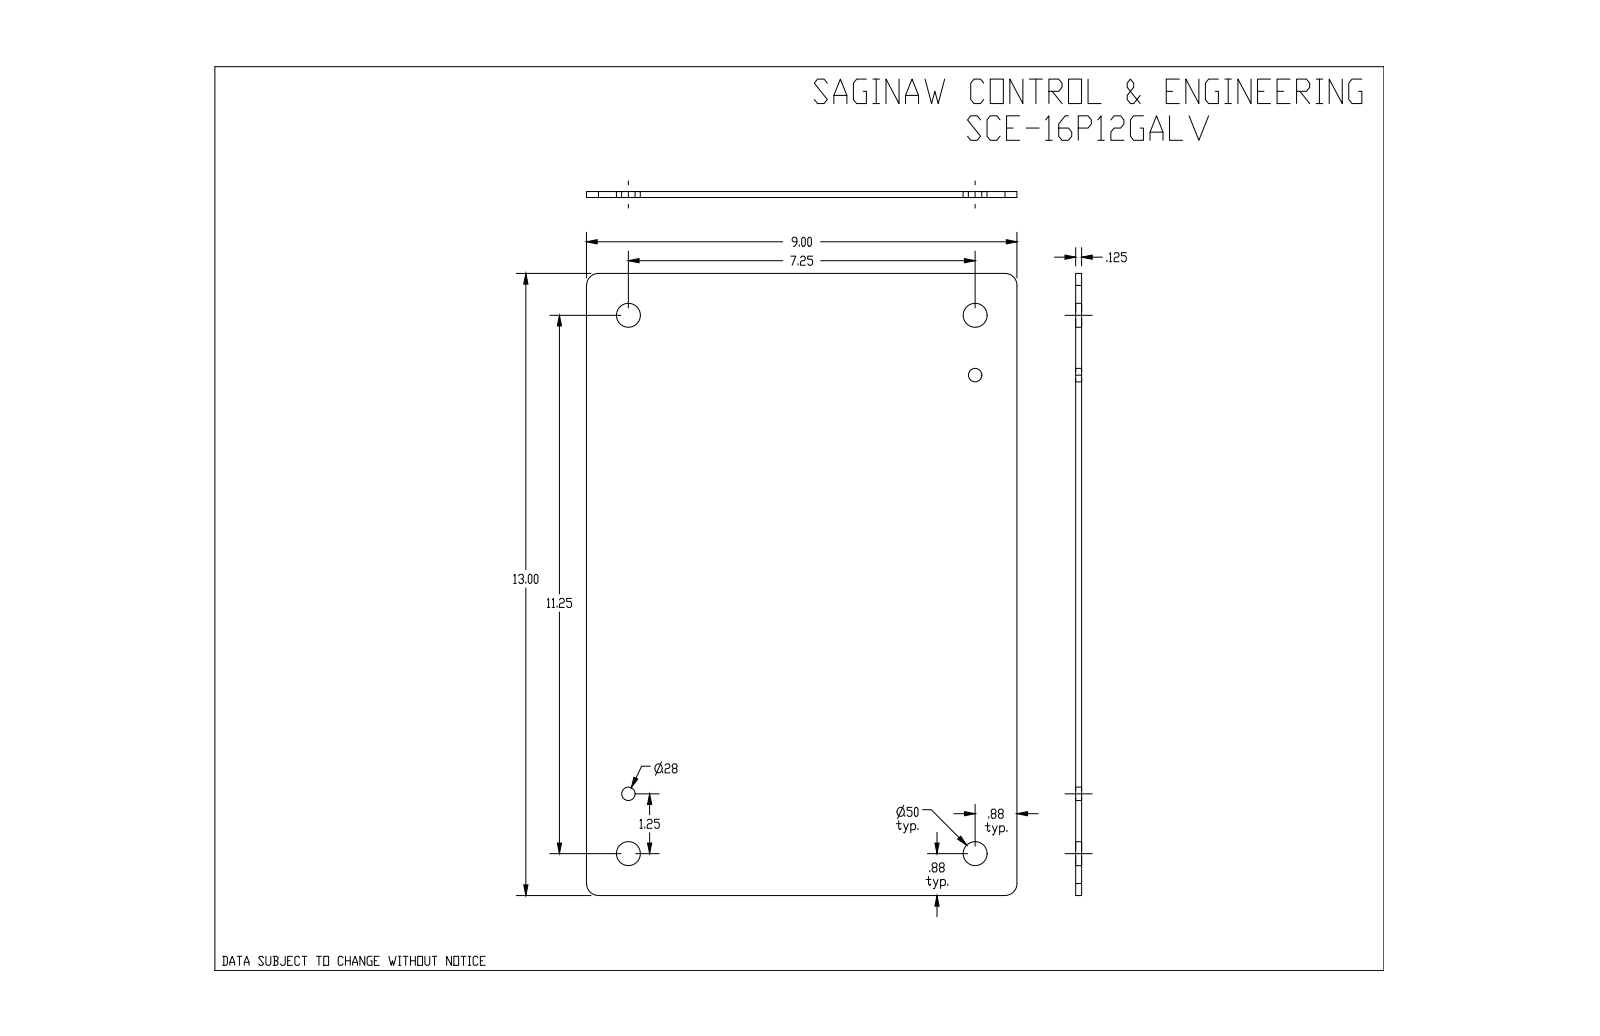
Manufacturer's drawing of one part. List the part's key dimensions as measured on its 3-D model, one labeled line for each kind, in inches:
Part name (STEP PRODUCT): SCE-16P12GALV
STEP written by: SolidWorks 2019 (CONFIG_CONTROL_DESIGN)
Units: inches
Bodies: 1 solid, 16 faces (6 planar, 10 cylindrical, 0 other)
Overall size (bounding box): 13 × 9 × 0.125
Volume: 14.5 in³ · Surface area: 238.5 in²
Round holes (diameter × count): ⌀0.5 ×4, ⌀0.281 ×1, ⌀0.281 ×1
Partial cylindrical surfaces — rounded edges, fillets, slot ends (radius × count): R0.25 ×4
Main face-to-face distances: 0.125, 9, 13
Hole centre spacings: 1.25, 7.25, 7.357, 10, 11.25, 12.352, 13.384, 11.363
